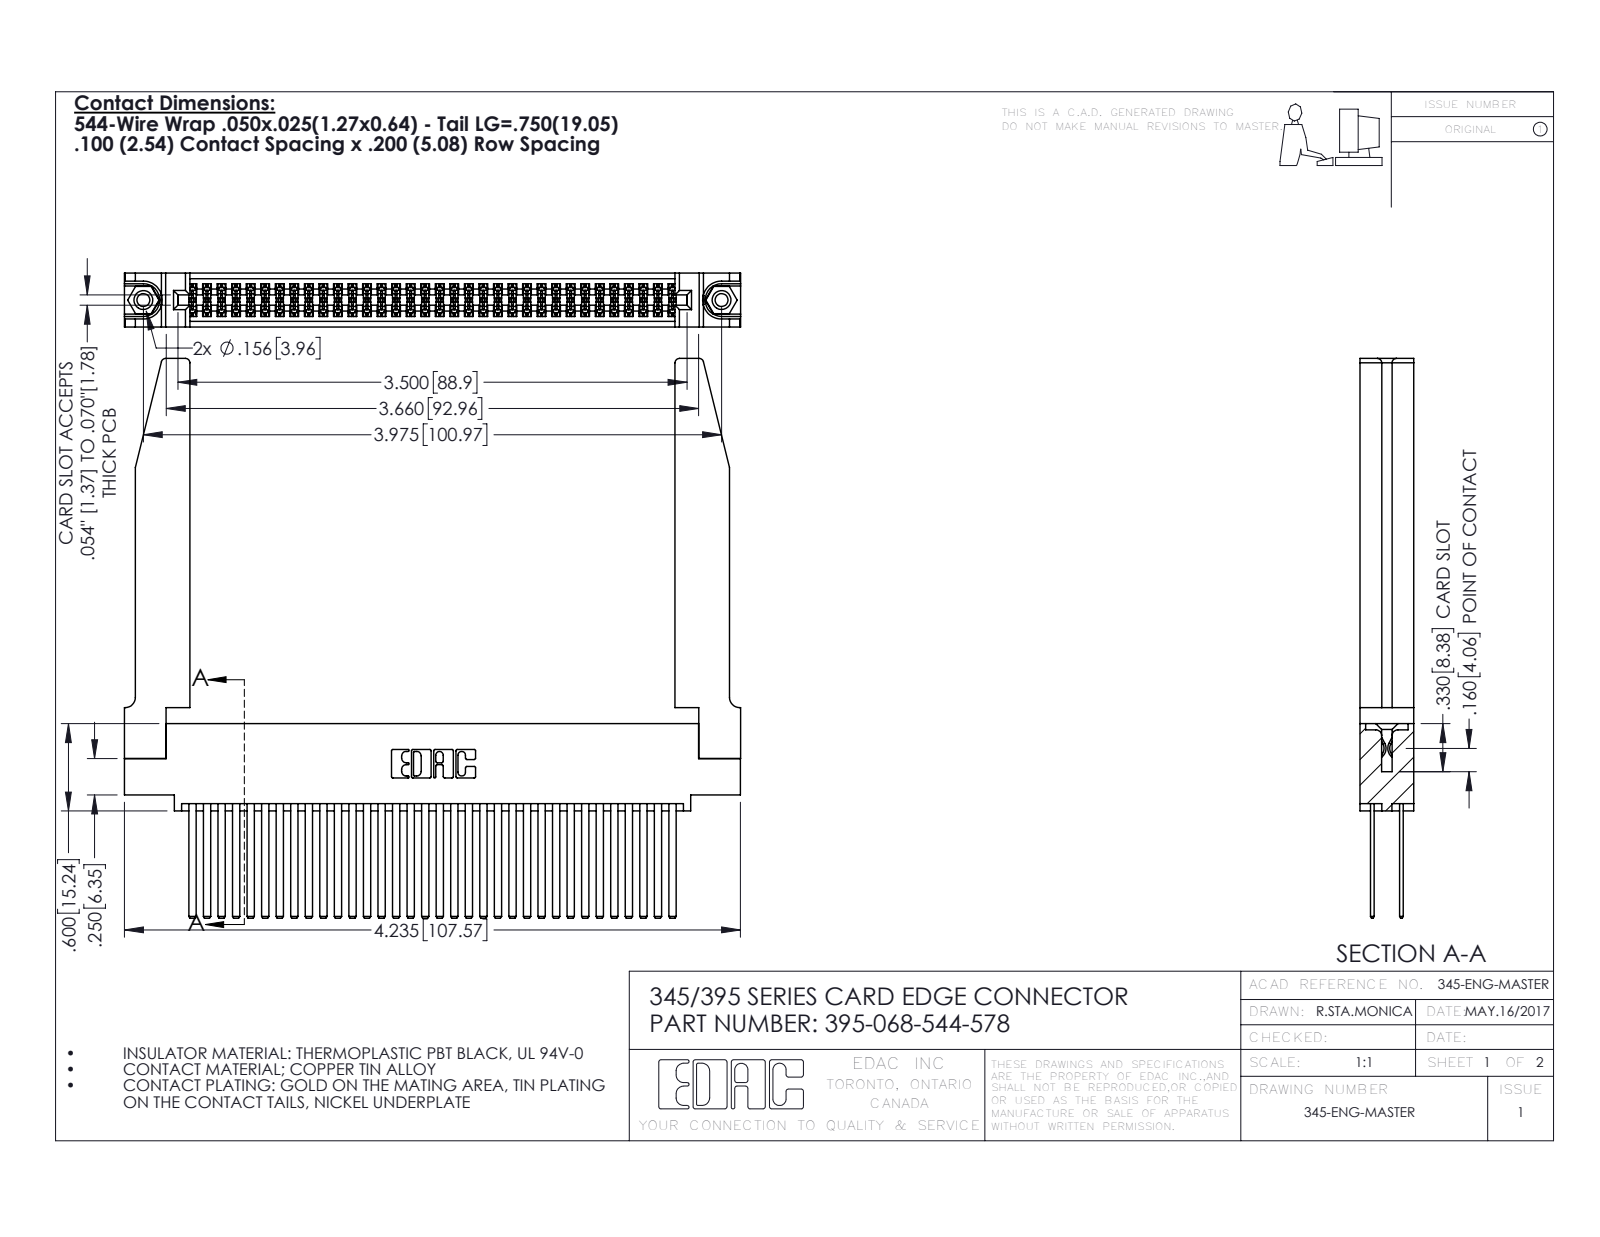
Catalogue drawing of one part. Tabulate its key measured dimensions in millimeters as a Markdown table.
| quantity | value |
| --- | --- |
| part name | 345 Part_0.110 Offset - 0.156 Dia-TH; 345-292-001_345-293-144; 395-068-544-578; 345-220-078_345-220-078 (+1 more) |
| STEP written by | SolidWorks 2016 (CONFIG_CONTROL_DESIGN) |
| units | millimeters |
| bodies | 73 solids, 3356 faces (2198 planar, 1106 cylindrical, 52 other) |
| overall size | 107.6 × 97.7 × 9.4 |
| volume | 19 030 mm³ |
| surface area | 26 210 mm² |
| round holes (diameter × count) | 2.3 × 2, 3.2 × 2, 4 × 2, 1.6 × 1 |
| round bosses / shafts (diameter × count) | 3.9 × 2 |
| partial cylindrical surfaces (radius × count) | 0.2 × 102, 0.3 × 22, 0.8 × 8, 0.2 × 6, 0.8 × 6, 0.7 × 3, 0.4 × 2, 0.5 × 2 |
| main face-to-face distances | 1.8, 7.6, 2.5, 6.9, 0.6, 5.1, 9.4, 5.7, 4.4, 3.8 |
| hole center spacings | 6.9, 95, 101 |
